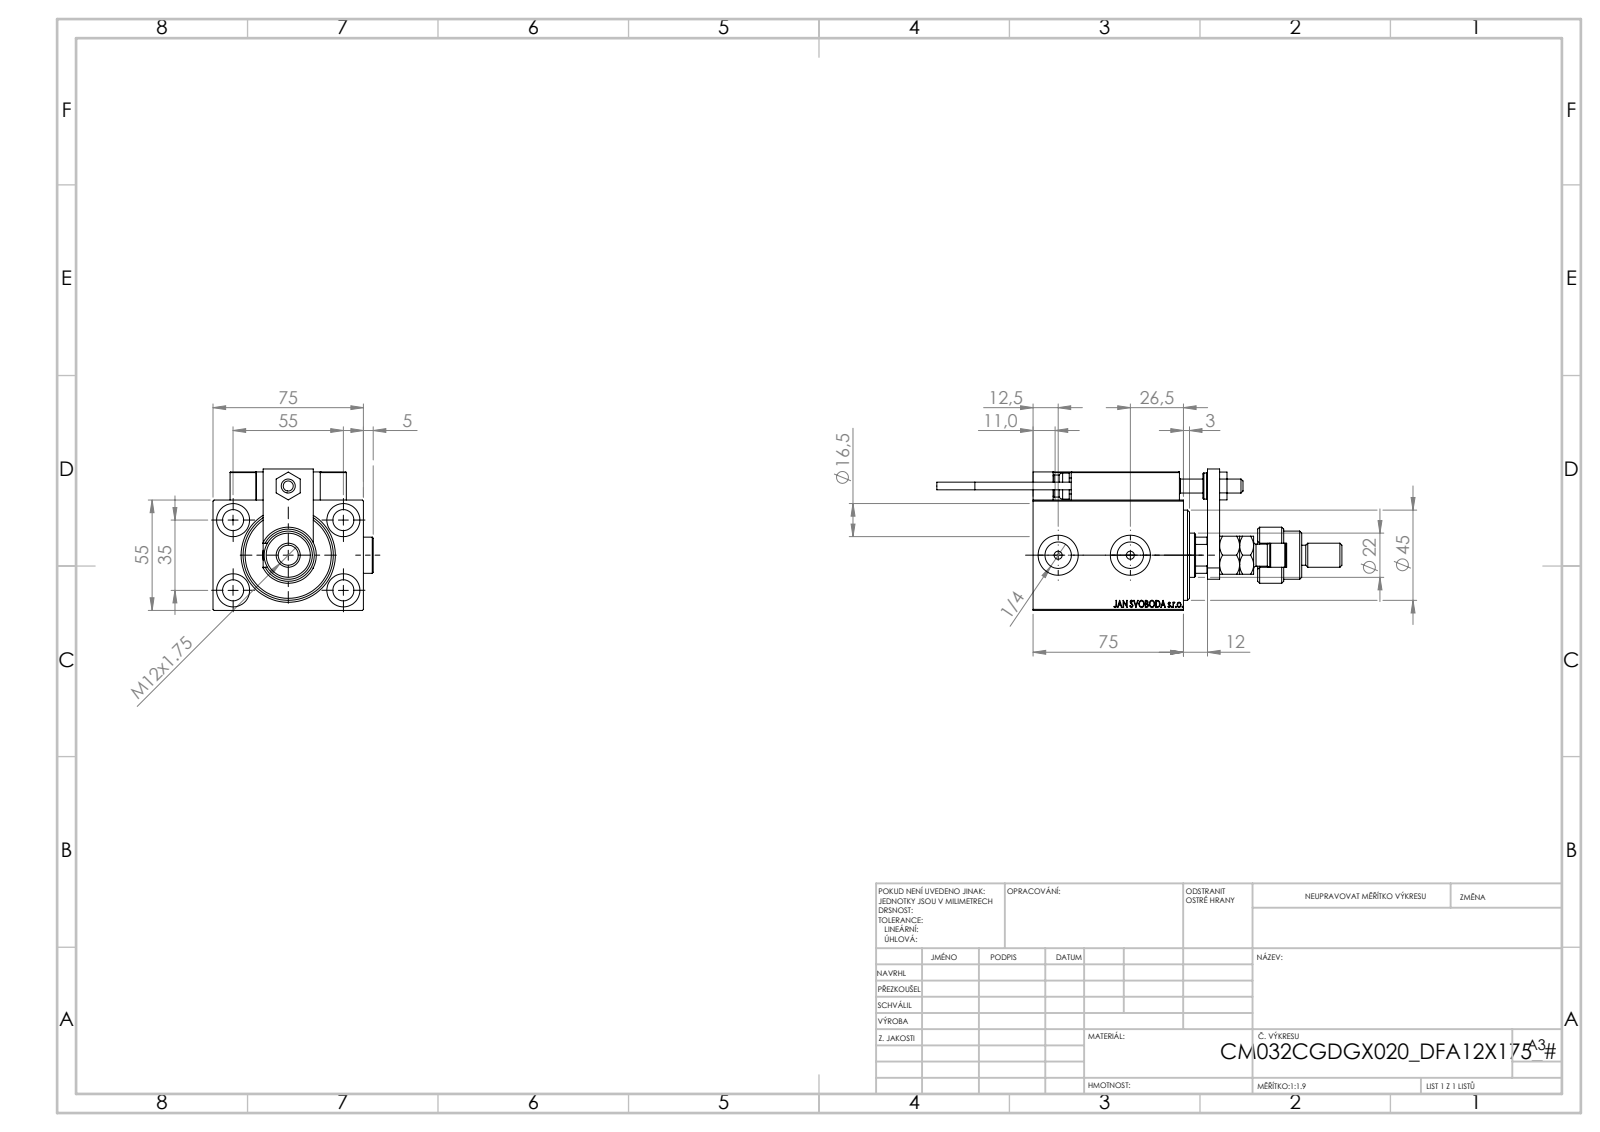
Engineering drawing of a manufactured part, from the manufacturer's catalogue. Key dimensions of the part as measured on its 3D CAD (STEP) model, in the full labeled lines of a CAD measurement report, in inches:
Part name (STEP PRODUCT): MAGNET; ZARAZKA; SWITCH X; MFA (+8 more)
STEP written by: SolidWorks 2019 (CONFIG_CONTROL_DESIGN)
Units: inches
Bodies: 27 solids, 1421 faces (622 planar, 217 cylindrical, 582 other)
Overall size (bounding box): 7.953 × 3.146 × 2.776
Volume: 20.11 in³ · Surface area: 146.5 in²
Round holes (diameter × count): ⌀0.157 ×6, ⌀0.315 ×5, ⌀0.413 ×5, ⌀0.65 ×5, ⌀0.126 ×4, ⌀0.197 ×2, ⌀0.518 ×2, ⌀0.787 ×2, ⌀0.276 ×1, ⌀0.866 ×1, ⌀1.004 ×1, ⌀1.26 ×1
Round bosses / shafts (diameter × count): ⌀0.709 ×3, ⌀0.433 ×2, ⌀0.197 ×2, ⌀0.15 ×2, ⌀1.102 ×1, ⌀0.945 ×1, ⌀0.512 ×1, ⌀0.472 ×1
Partial cylindrical surfaces — rounded edges, fillets, slot ends (radius × count): R0.012 ×30, R0.118 ×2, R0.384 ×1, R0.413 ×1
Main face-to-face distances: 2.165, 2.953, 0.551, 0.394, 0.472, 0.709, 2.717, 0.984, 0.197, 0.236
Hole centre spacings: 1.283, 0.448, 0.787, 1.066, 1.165, 1.169, 1.273, 1.371
